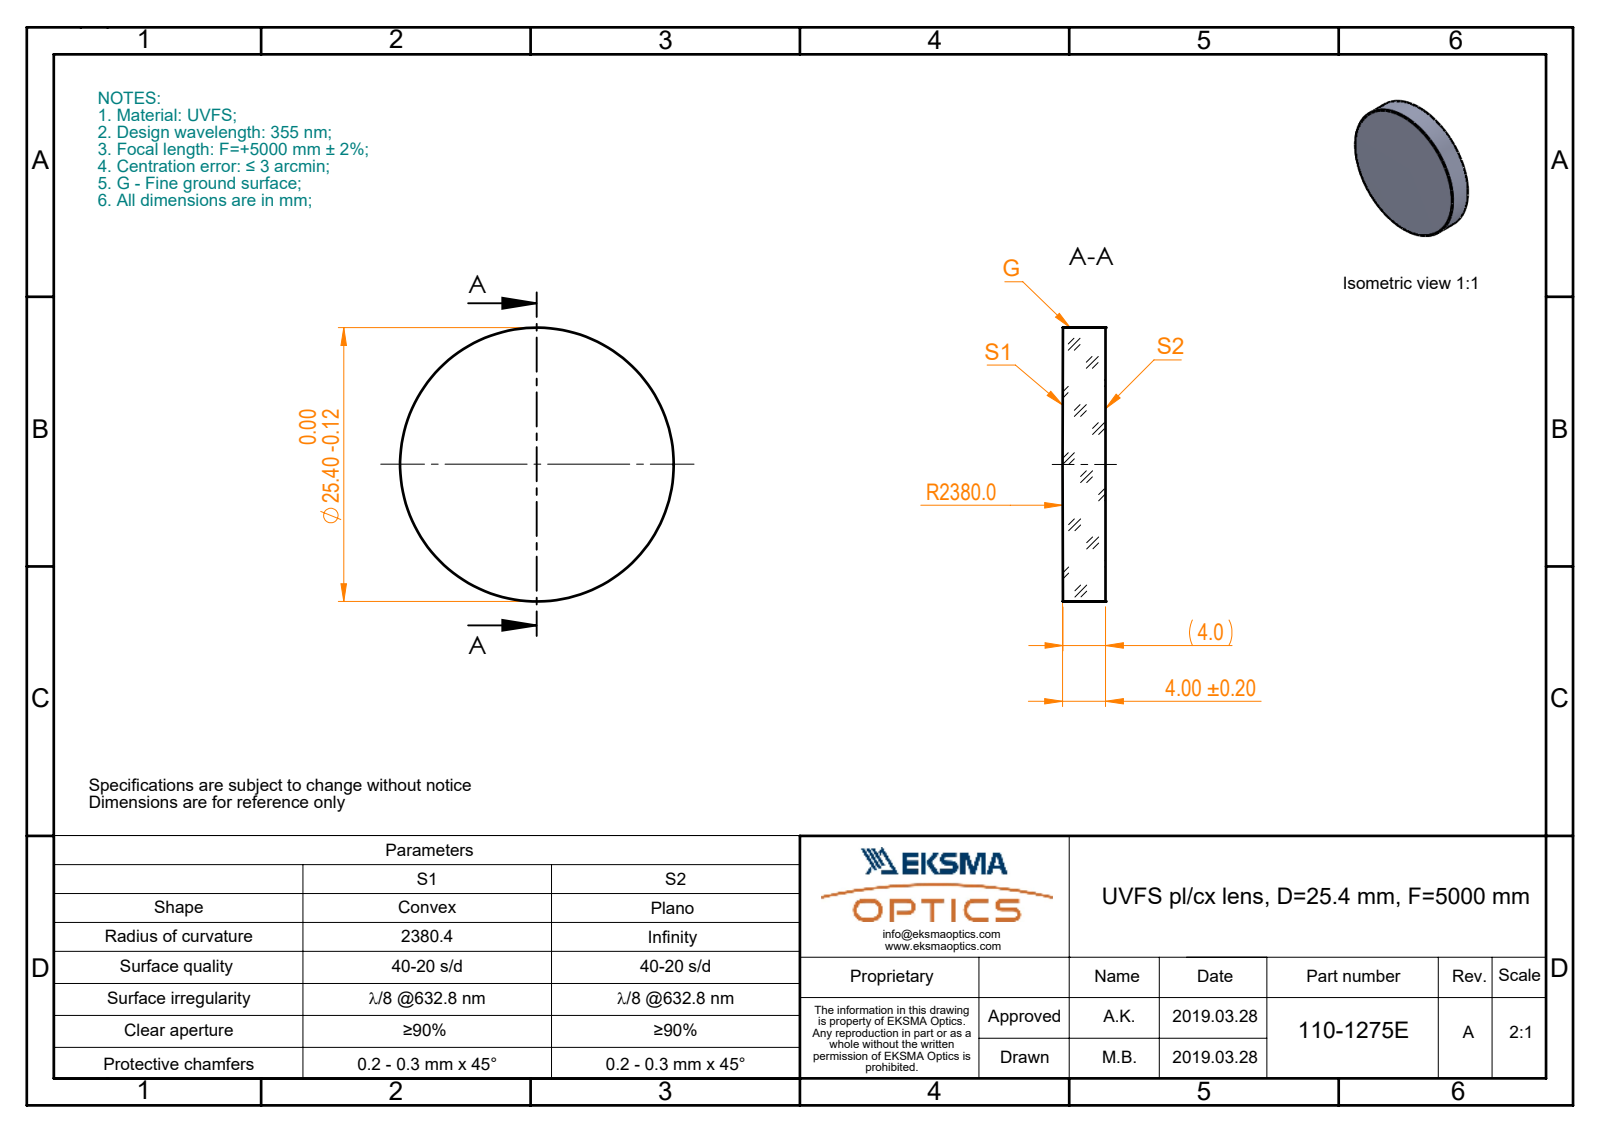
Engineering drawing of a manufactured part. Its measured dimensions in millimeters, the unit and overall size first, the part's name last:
Units: millimetres
Overall size (bounding box): 25.4 × 25.4 × 4
Round bosses / shafts (diameter × count): ⌀25.4 ×1
Volume: 2 018 mm³ · Surface area: 1 330 mm²
Bodies: 1 solid, 5 faces (1 planar, 2 cylindrical, 2 other)
Part name (STEP PRODUCT): 110-1275E UVFS pl-cx 25.4 F5000
STEP written by: SolidWorks 2017 (CONFIG_CONTROL_DESIGN)
